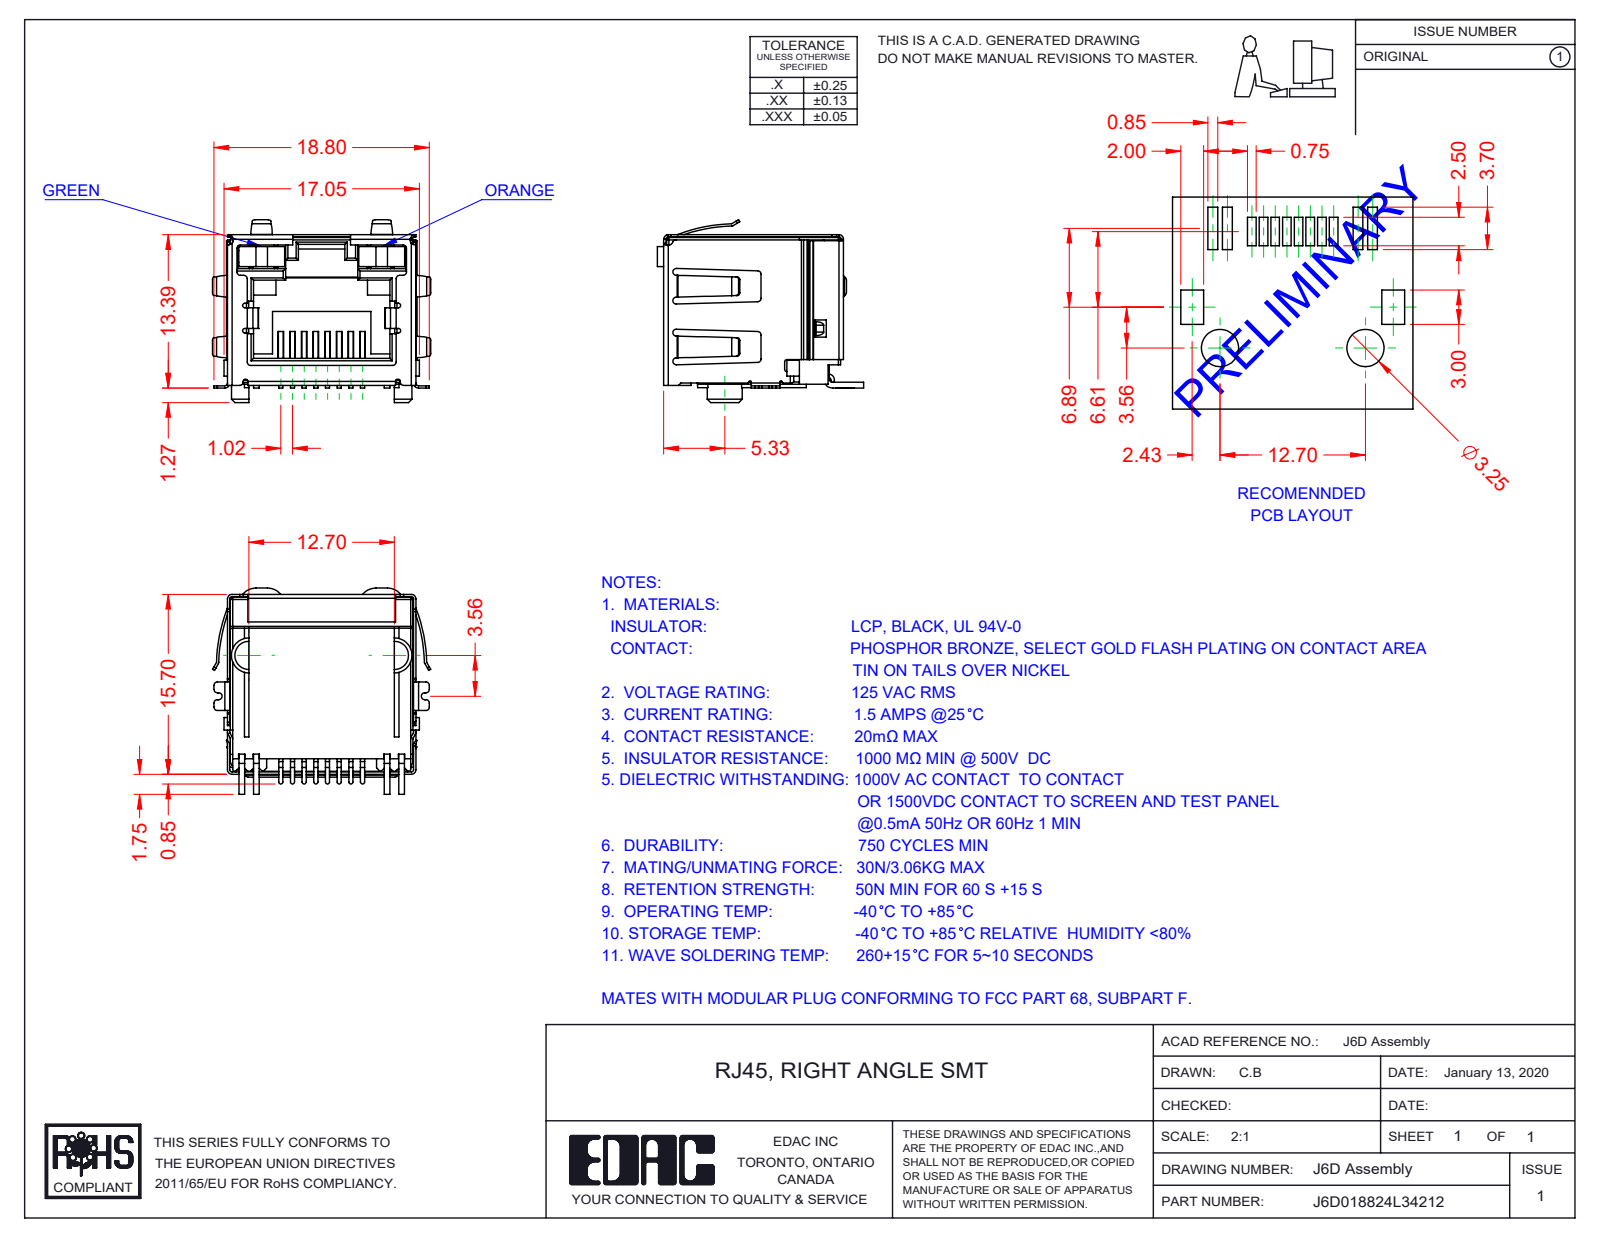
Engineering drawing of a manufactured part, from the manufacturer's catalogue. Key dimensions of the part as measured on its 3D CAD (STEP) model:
Part name (STEP PRODUCT): J6D018824L34212; 6D Shield_LED - EMI; 6D LED RH_4-Orange; 6D LED LH_3-Green (+2 more)
STEP written by: SolidWorks 2016 (CONFIG_CONTROL_DESIGN)
Units: millimetres
Bodies: 12 solids, 1028 faces (701 planar, 282 cylindrical, 45 other)
Overall size (bounding box): 19.06 × 18 × 15.95
Volume: 1 790 mm³ · Surface area: 4 796 mm²
Partial cylindrical surfaces — rounded edges, fillets, slot ends (radius × count): R0.3 ×55, R0.2 ×40, R0.4 ×19, R0.25 ×16, R0.1 ×12, R0.15 ×8, R0.18 ×8, R0.5 ×6
Main face-to-face distances: 16, 16.2, 16.25, 2.25, 1, 15.95, 12.8, 0.45, 13.05, 10.6
